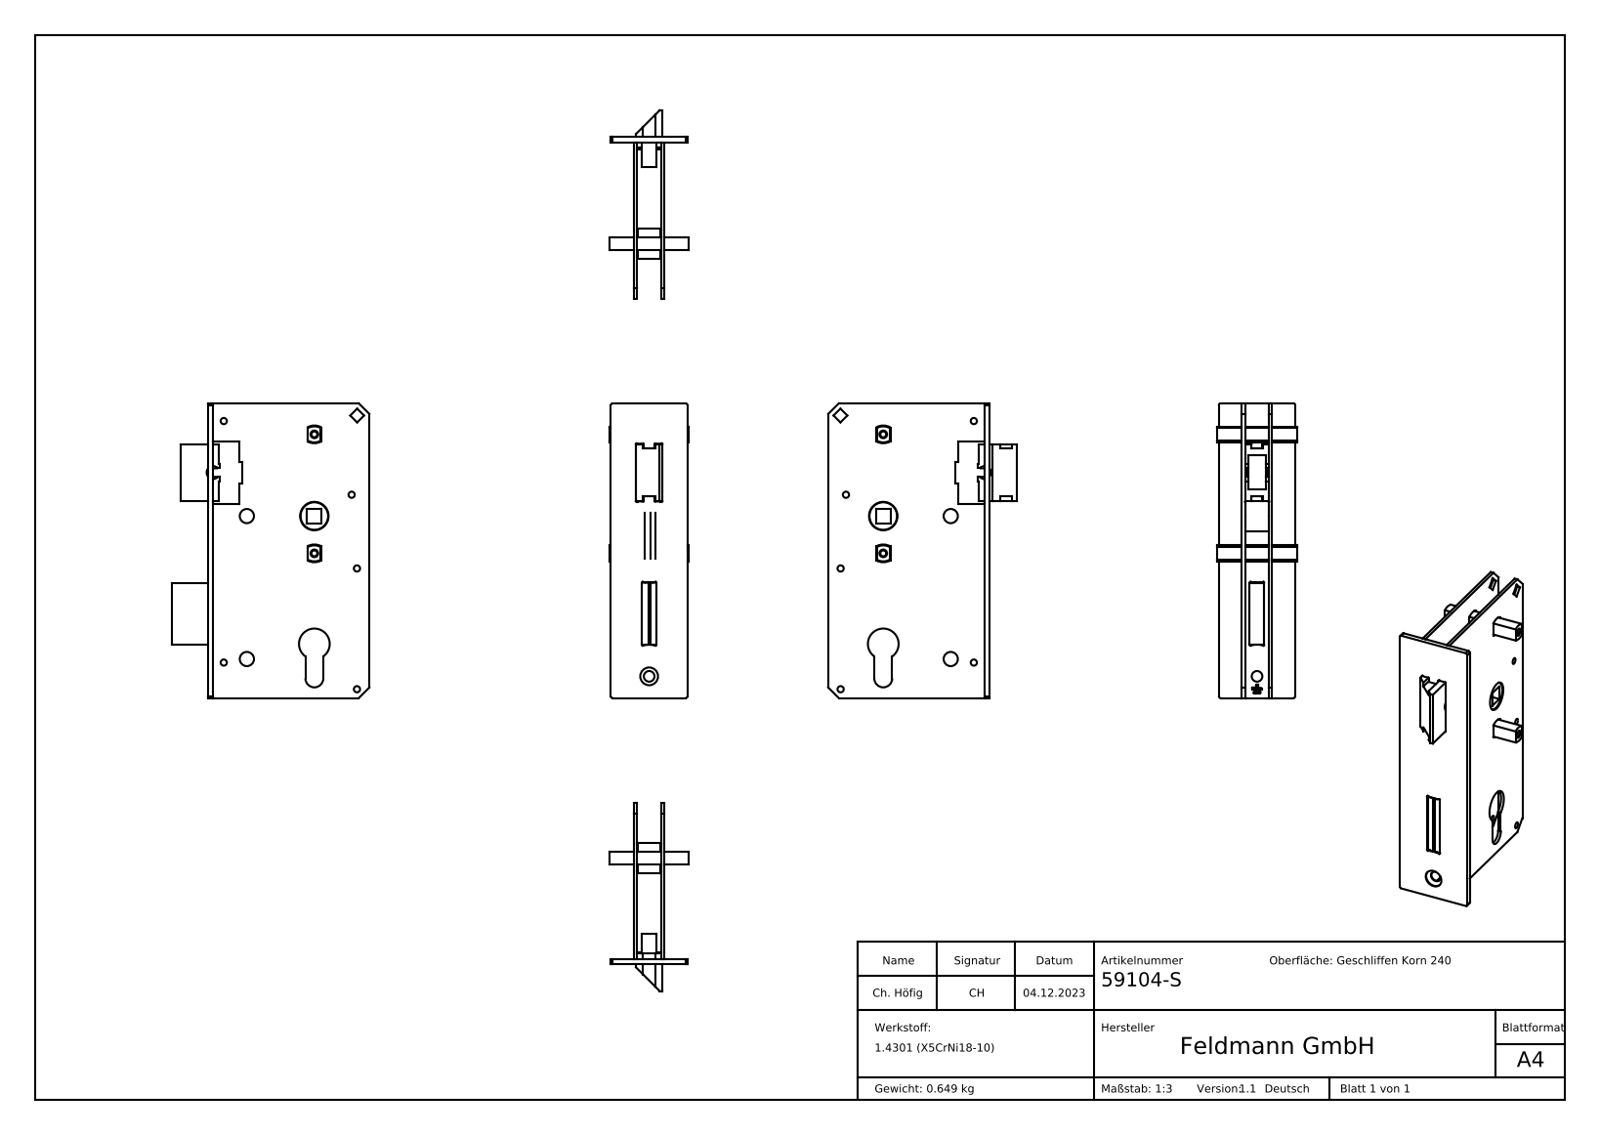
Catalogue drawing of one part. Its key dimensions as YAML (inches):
part_name: "Schlosskasten Teil4 Konfig_59XXX-240 Teil4; Schlosskasten Teil3 Konfig_59XXX-240 Teil3; Schlosskasten Teil2 Konfig_59104-240 Teil2; Schlosskasten Teil5 Konfig_59XXX-240 Teil5 (+1 more)"
step_written_by: "SolidWorks 2018 (CONFIG_CONTROL_DESIGN)"
units: inches
bodies: {solids: 8, faces: 454, planar: 261, cylindrical: 71, other: 122}
overall_size: [6.535, 4.173, 1.772]
volume: 5.004
surface_area: 124.1
round_holes:
  - {diameter: 0.138, count: 5}
  - {diameter: 0.13, count: 2}
  - {diameter: 0.315, count: 2}
  - {diameter: 0.236, count: 1}
  - {diameter: 0.394, count: 1}
  - {diameter: 0.63, count: 1}
  - {diameter: 0.681, count: 1}
round_bosses_or_shafts:
  - {diameter: 0.669, count: 1}
  - {diameter: 0.61, count: 1}
partial_cylinders:
  - {radius: 0.012, count: 8}
  - {radius: 0.024, count: 8}
  - {radius: 0.02, count: 4}
  - {radius: 0.039, count: 4}
  - {radius: 0.173, count: 4}
  - {radius: 0.295, count: 4}
  - {radius: 0.315, count: 4}
  - {radius: 0.094, count: 1}
face_to_face_distances: [0.069, 0.6, 0.669, 0.531, 0.118, 0.581, 1.181, 0.512, 1.112, 0.134]
hole_center_spacings: [0.518, 0.827, 0.952, 1.002, 1.379, 1.496, 1.497, 1.533]
